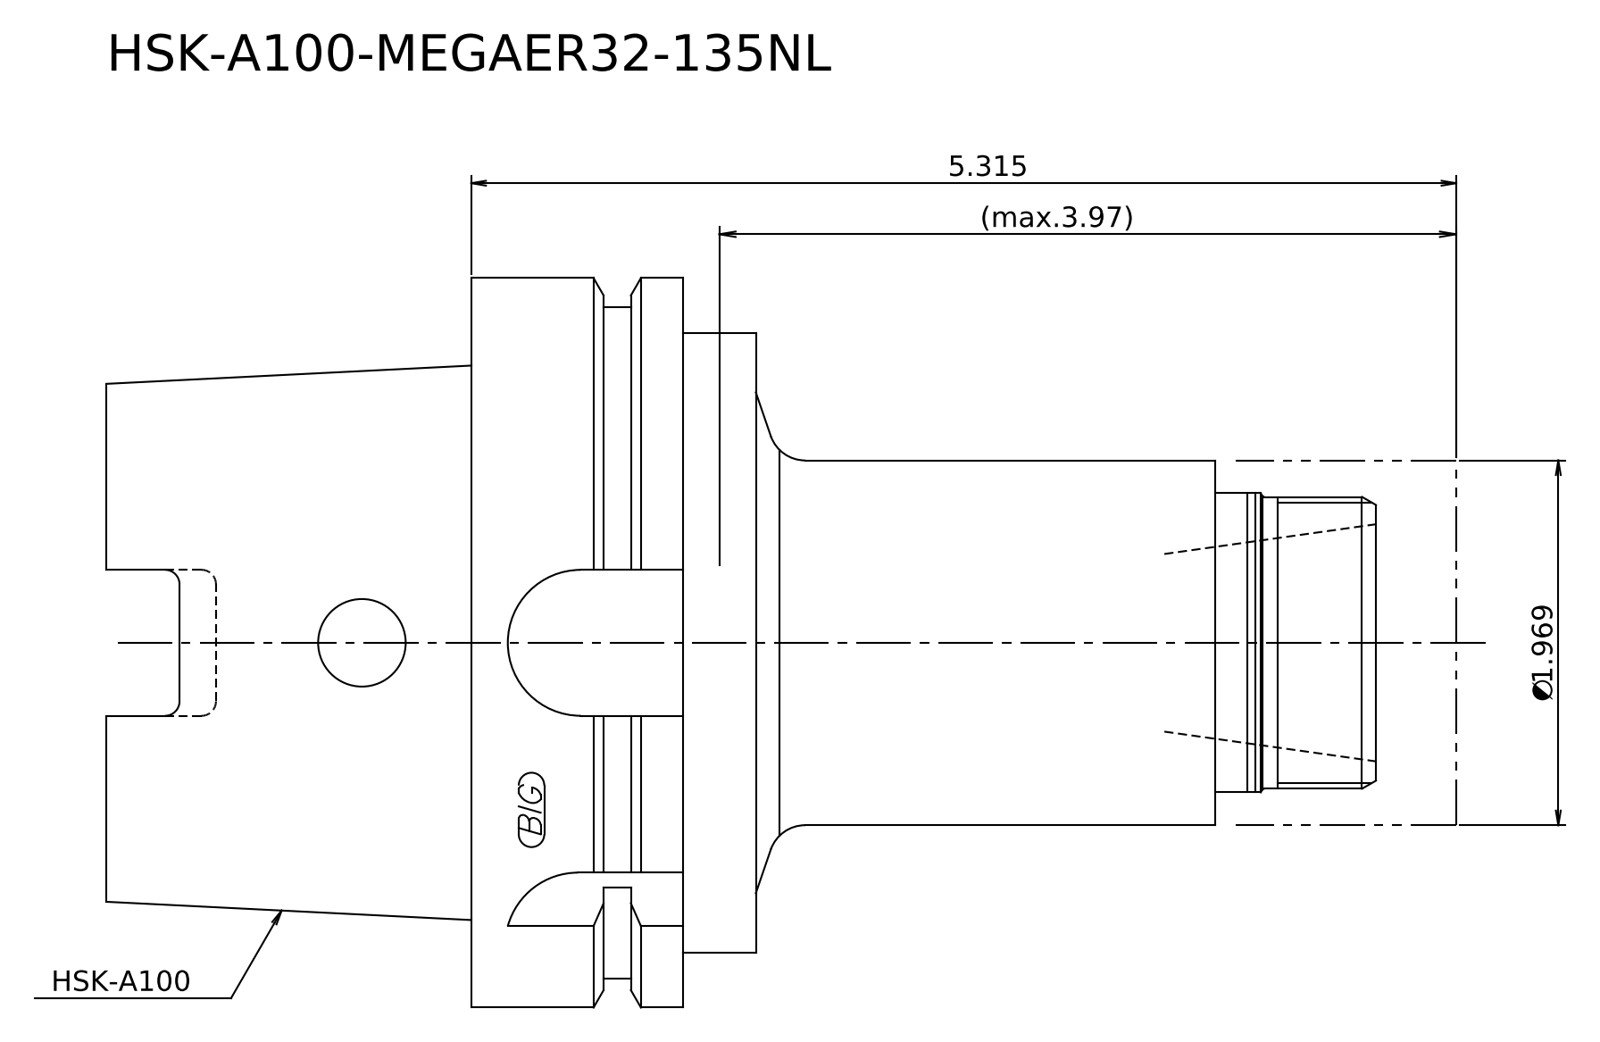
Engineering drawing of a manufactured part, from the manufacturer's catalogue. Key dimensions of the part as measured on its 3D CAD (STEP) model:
STEP written by: Kubotek KeyCreator 2011 V10.0.2 (22737) (automotive_design)
Units: millimetres
Bodies: 2 solids, 24 faces (10 planar, 8 cylindrical, 6 other)
Overall size (bounding box): 185 × 100 × 100
Volume: 707 698 mm³ · Surface area: 60 709 mm²
Round bosses / shafts (diameter × count): ⌀100 ×1, ⌀92 ×1, ⌀85 ×1, ⌀50 ×1, ⌀41 ×1, ⌀40 ×1
Main face-to-face distances: 50, 29, 79, 10, 39, 89, 65.8, 75.8, 104.8, 154.8
